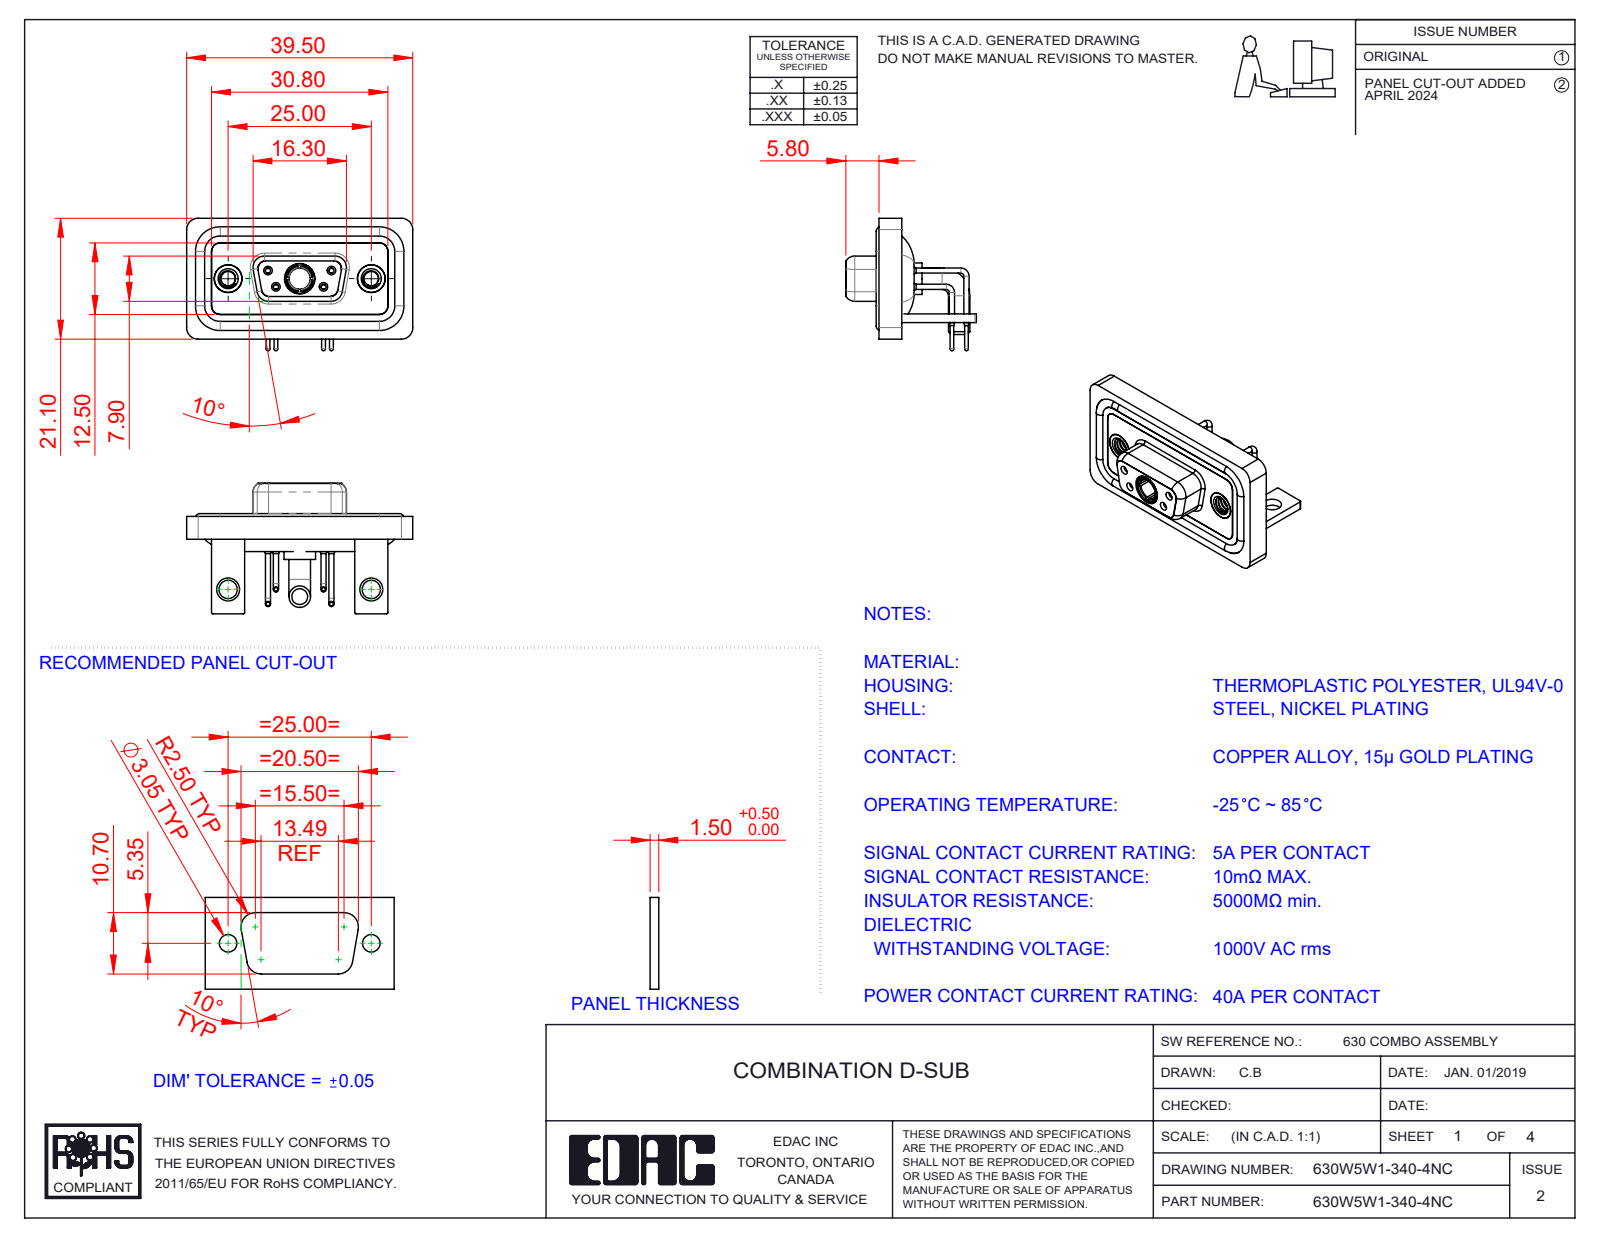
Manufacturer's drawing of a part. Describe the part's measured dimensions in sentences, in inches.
The part is named "630Combo Waterproof Housing_09 Contacts; 630Combo Stabilizer Bracket_50 Contacts; 630Combo Contact Row 2_50 Contacts; 630Combo Threaded Rivet_A (+6 more)". Its 3-D file was written by "SolidWorks 2023 (CONFIG_CONTROL_DESIGN)". It is 15 solids with 718 faces: 214 planar, 327 cylindrical and 177 other. Overall it measures 1.555 by 0.91 by 0.898 inches. Its volume is 0.321 cubic inches and its surface area 13.37 square inches. Round holes: 4 of diameter 0.035, 4 of diameter 0.043, 4 of diameter 0.059, 4 of diameter 0.079, 3 of diameter 0.191, 2 of diameter 0.063, 2 of diameter 0.067, 2 of diameter 0.098, 2 of diameter 0.126, 2 of diameter 0.157, 2 of diameter 0.159, 2 of diameter 0.197. Round bosses or shafts: 6 of diameter 0.063, 4 of diameter 0.035, 4 of diameter 0.026, 2 of diameter 0.195, 2 of diameter 0.189, 2 of diameter 0.148, 1 of diameter 0.217, 1 of diameter 0.205. Partial cylindrical surfaces (rounded edges, fillets, slot ends): 19 of radius 0.079, 18 of radius 0.059, 16 of radius 0.01, 8 of radius 0.053, 8 of radius 0.063, 5 of radius 0.02, 4 of radius 0.024, 4 of radius 0.026. The main face-to-face distances are 0.016, 0.114, 0.059, 0.071, 0.043, 0.146, 0.063, 0.031, 0.098, 0.122. The hole center spacings are 0.124, 0.225, 0.28, 0.492, 0.713, 0.984, 0.173, 0.173.
